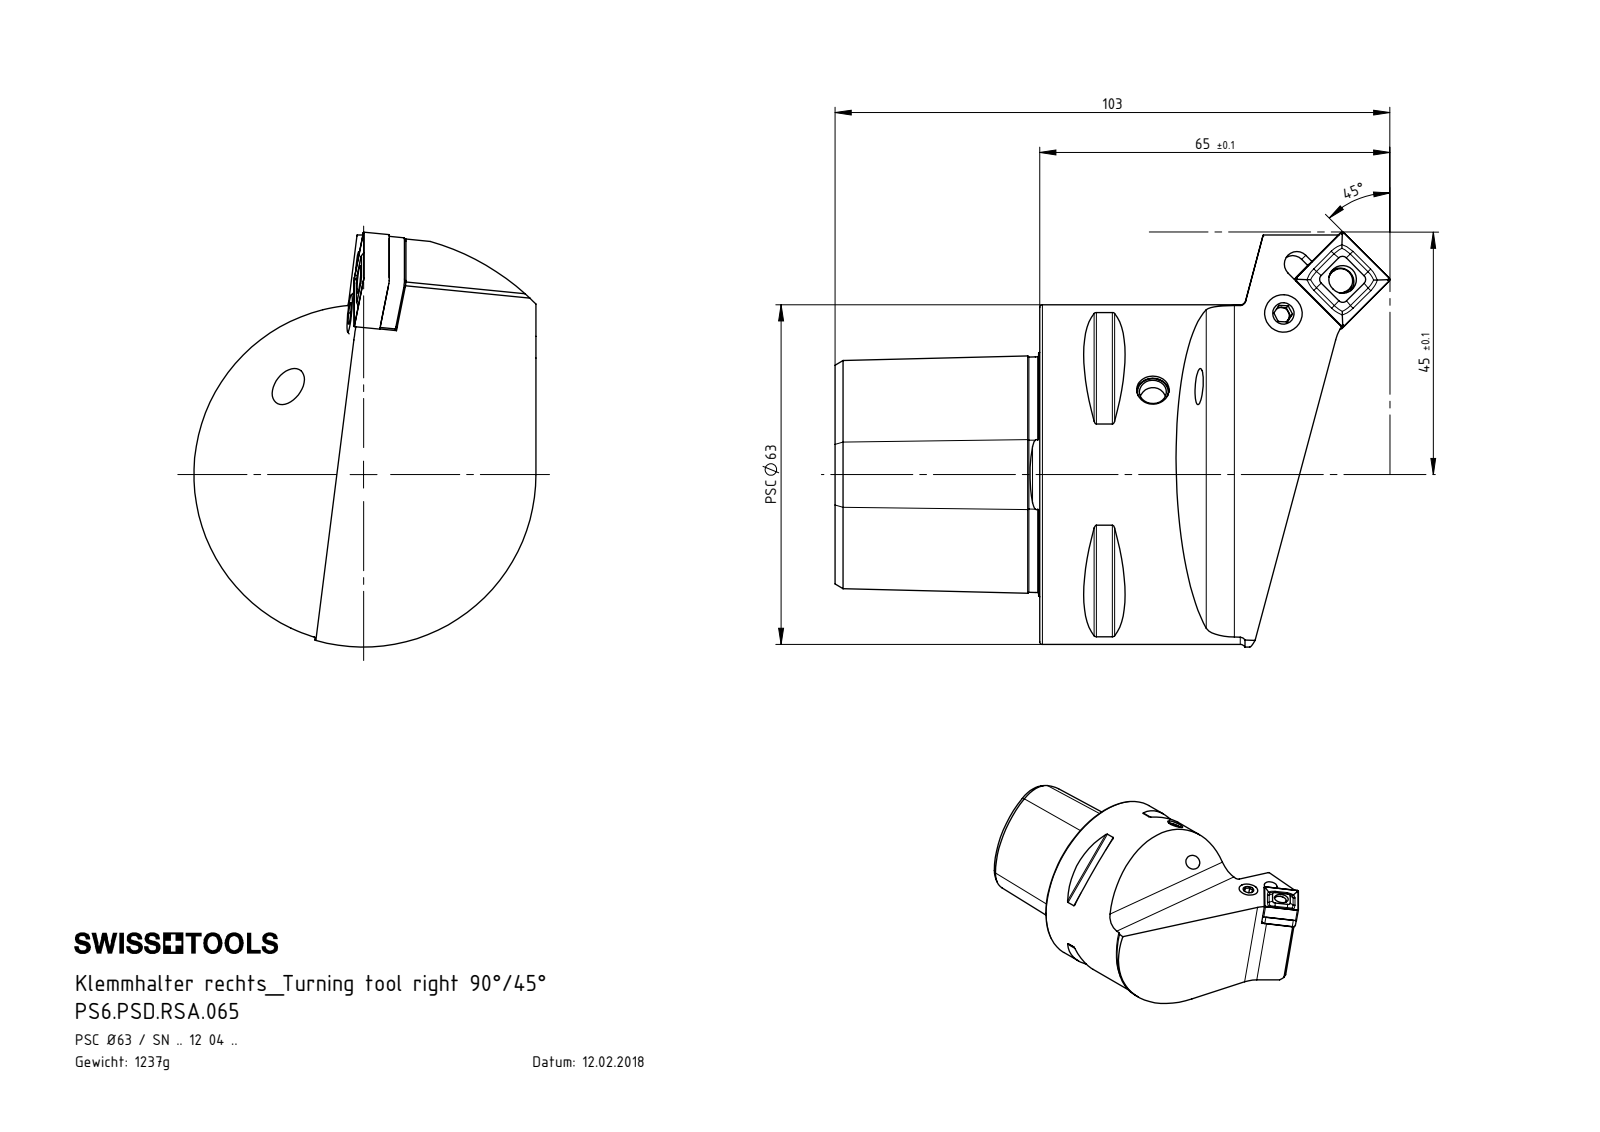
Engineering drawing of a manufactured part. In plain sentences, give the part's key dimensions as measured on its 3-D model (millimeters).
The part is named "SNMG120404; WCD-ER1.101.000; KVT_MB_600_060; PS6.PSD.RSA.065 (+4 more)". Its 3-D file was written by "SolidWorks 2017 (AUTOMOTIVE_DESIGN)". It is 8 solids with 337 faces: 90 planar, 83 cylindrical and 164 other. Overall it measures 103 by 77 by 63.5 millimeters. Its volume is 157 116 cubic millimeters and its surface area 30 313 square millimeters. Round holes: 2 of diameter 5, 1 of diameter 4, 1 of diameter 5.16, 1 of diameter 6.4, 1 of diameter 7, 1 of diameter 8.1, 1 of diameter 8.4, 1 of diameter 18, 1 of diameter 28, 1 of diameter 32. Round bosses or shafts: 1 of diameter 63, 1 of diameter 8, 1 of diameter 7.9, 1 of diameter 6.4, 1 of diameter 6, 1 of diameter 4.5, 1 of diameter 3.55. Partial cylindrical surfaces (rounded edges, fillets, slot ends): 8 of radius 0.5, 4 of radius 0.4, 4 of radius 1.2, 2 of radius 2.5, 2 of radius 6, 1 of radius 2.2, 1 of radius 2.35, 1 of radius 2.8. The main face-to-face distances are 38, 24.88, 4.45, 27, 11, 3.18, 7.63, 55.8, 12.19, 12.7. The hole center spacings are 12.8, 12.81, 27.5.
